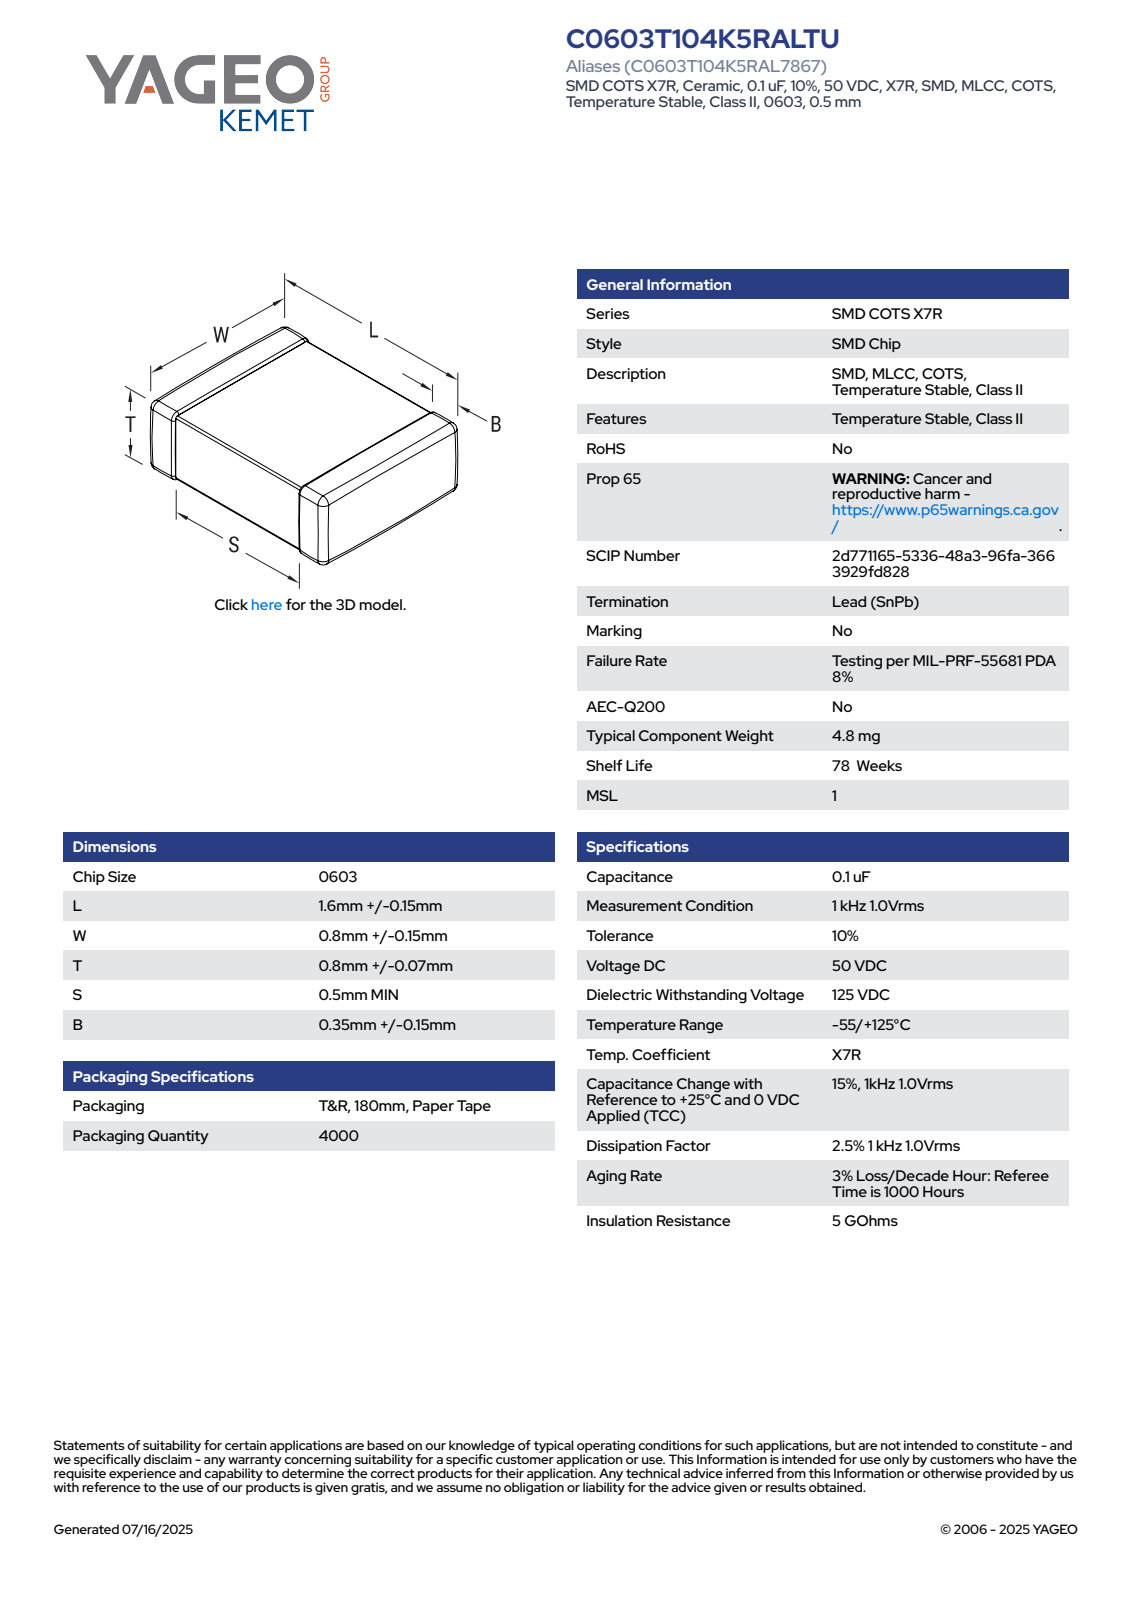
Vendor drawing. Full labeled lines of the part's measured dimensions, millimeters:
Part name (STEP PRODUCT): CCSM_STD_0603_L1.75W0.95T0.87B0.5
STEP written by: SolidWorks 2014 (AUTOMOTIVE_DESIGN)
Units: millimetres
Bodies: 4 solids, 125 faces (71 planar, 38 cylindrical, 16 other)
Overall size (bounding box): 1.75 × 0.95 × 0.87
Volume: 1 mm³ · Surface area: 8 mm²
Main face-to-face distances: 0.85, 0.93, 0.87, 0.95, 1.75, 0.83, 0.91, 0.86, 0.84, 0.52
